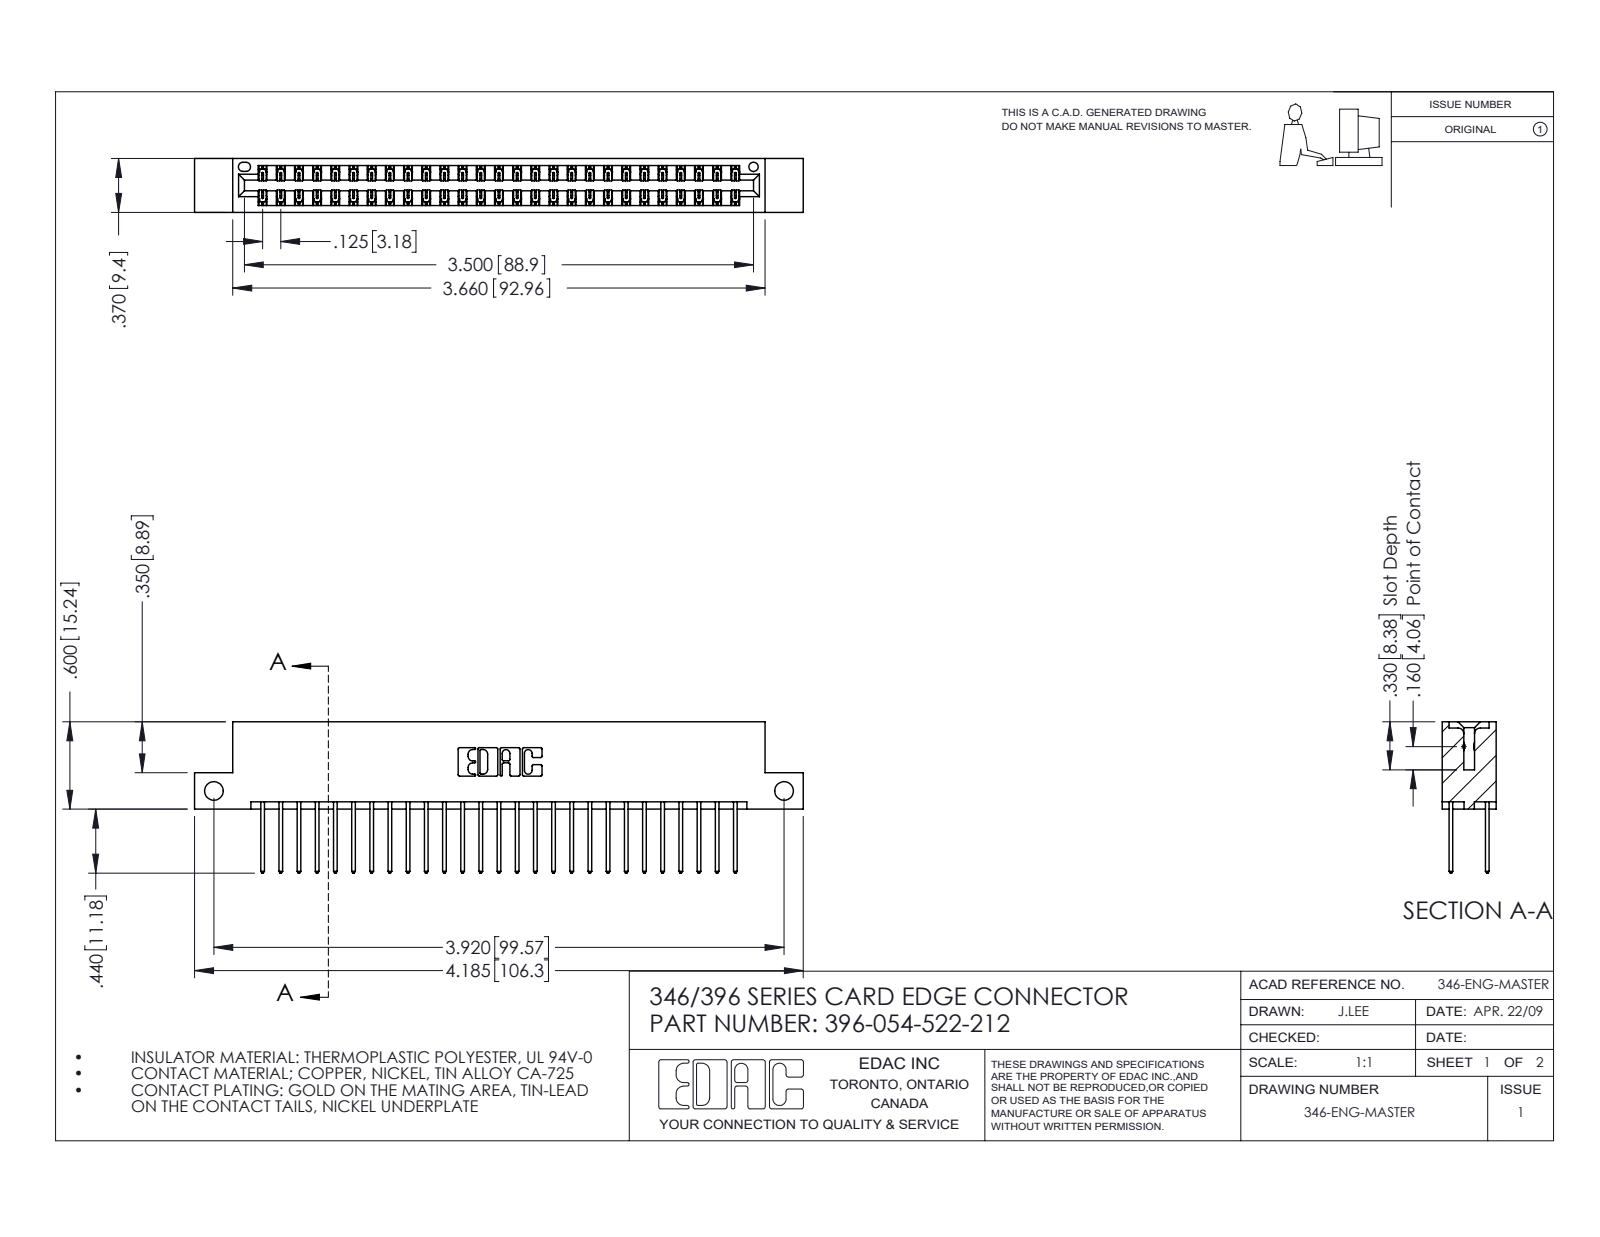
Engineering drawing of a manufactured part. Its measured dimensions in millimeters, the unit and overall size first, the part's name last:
Units: millimetres
Overall size (bounding box): 106.3 × 26.4 × 9.4
Round holes (diameter × count): ⌀3.3 ×2, ⌀1.6 ×1
Partial cylindrical surfaces — rounded edges, fillets, slot ends (radius × count): R0.2 ×81, R0.3 ×54, R0.3 ×22, R0.2 ×6, R0.8 ×6, R0.7 ×3, R0.4 ×2, R0.6 ×2
Main face-to-face distances: 1.2, 8.2, 6.4, 9.4, 1.8, 7.6, 0.6, 7, 3.8, 5.6
Hole centre spacings: 99.6
Volume: 10 300 mm³ · Surface area: 14 430 mm²
Bodies: 55 solids, 2930 faces (1966 planar, 964 cylindrical, 0 other)
Part name (STEP PRODUCT): 346 Part_Flush Mounting Lugs - Side Mount; 345-292-001_345-293-122; 396-054-522-212
STEP written by: SolidWorks 2016 (CONFIG_CONTROL_DESIGN)
